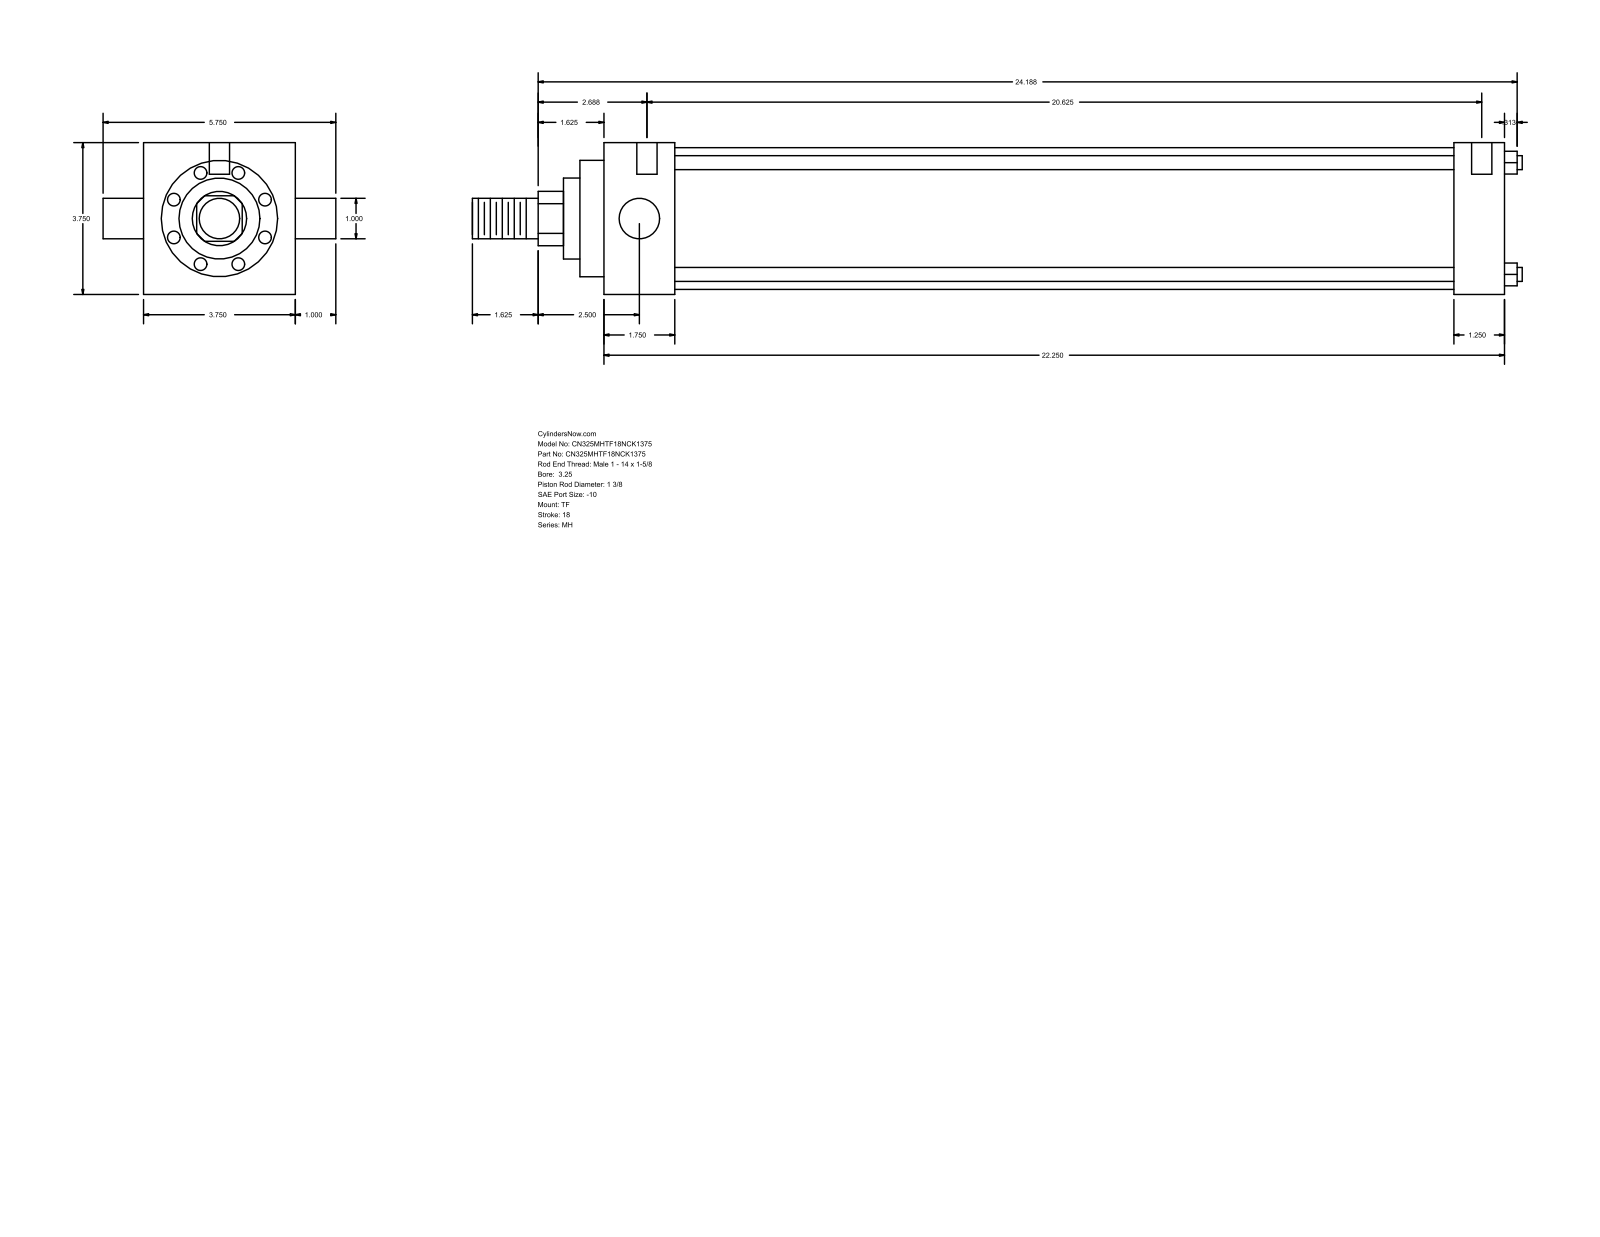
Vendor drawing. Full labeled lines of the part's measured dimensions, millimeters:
Part name (STEP PRODUCT): MH_TF__0325_1.375
STEP written by: GSSL Pune (CONFIG_CONTROL_DESIGN)
Units: millimetres
Bodies: 0 solids, 86 faces (61 planar, 25 cylindrical, 0 other)
Overall size (bounding box): 658.81 × 146.05 × 95.25
Round holes (diameter × count): ⌀5.56 ×3, ⌀12.7 ×2
Round bosses / shafts (diameter × count): ⌀8.76 ×4, ⌀25.4 ×2, ⌀88.9 ×1, ⌀73.03 ×1, ⌀50.8 ×1, ⌀34.92 ×1
Partial cylindrical surfaces — rounded edges, fillets, slot ends (radius × count): R17.06 ×1
Main face-to-face distances: 95.24, 565.15, 44.45, 533.4, 488.95, 520.7, 31.75, 15.08, 59.53, 548.48
Hole centre spacings: 1.59, 4.76, 523.88, 525.47, 528.64, 530.23
